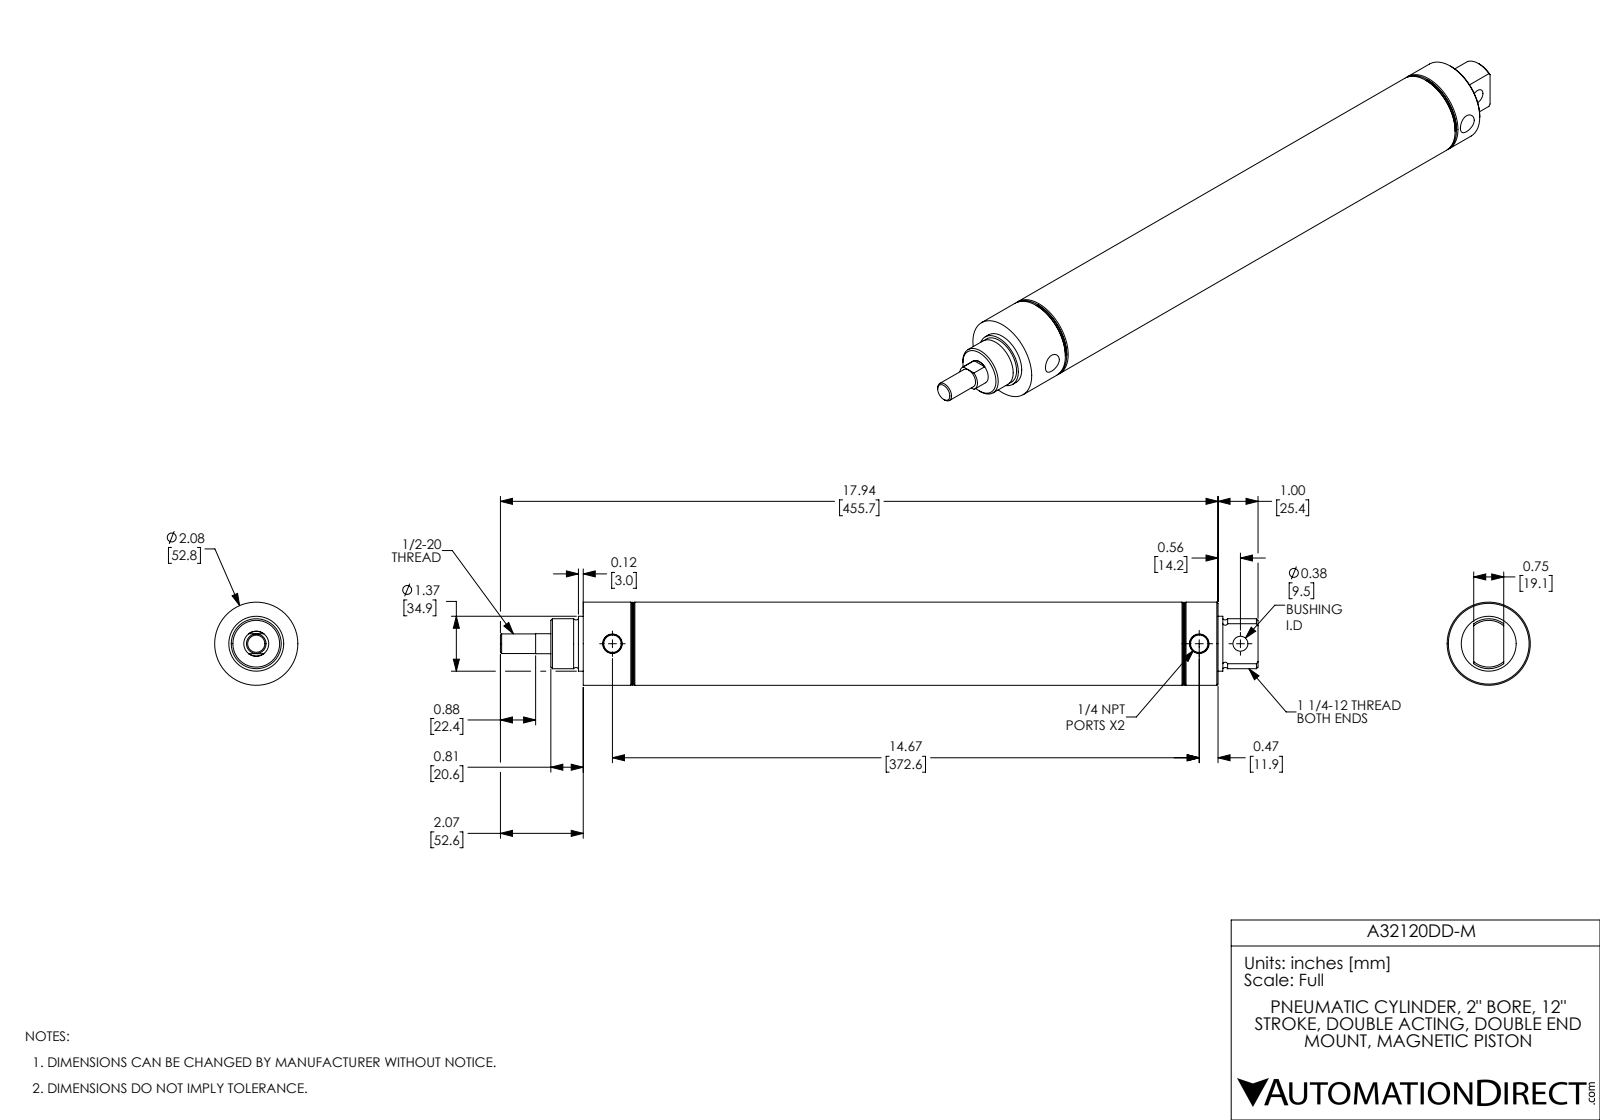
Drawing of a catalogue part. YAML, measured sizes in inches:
part_name: "A32120DD-M-MainBody; A32120DD-M-Rod; A32120DD-M"
step_written_by: "SolidWorks 2017 (AUTOMOTIVE_DESIGN)"
units: inches
bodies: {solids: 2, faces: 88, planar: 20, cylindrical: 30, other: 38}
overall_size: [18.94, 2.08, 2.08]
volume: 21.74
surface_area: 249.6
round_holes:
  - {diameter: 0.438, count: 2}
  - {diameter: 0.375, count: 1}
  - {diameter: 0.625, count: 1}
  - {diameter: 2, count: 1}
round_bosses_or_shafts:
  - {diameter: 2.08, count: 1}
  - {diameter: 1.373, count: 1}
  - {diameter: 1.25, count: 1}
  - {diameter: 0.491, count: 1}
face_to_face_distances: [0.5, 12.5, 12, 14.185, 13.685, 1.685, 1.685, 2.185, 14.185, 15.87]
hole_center_spacings: [1.03, 14.67, 15.7]
